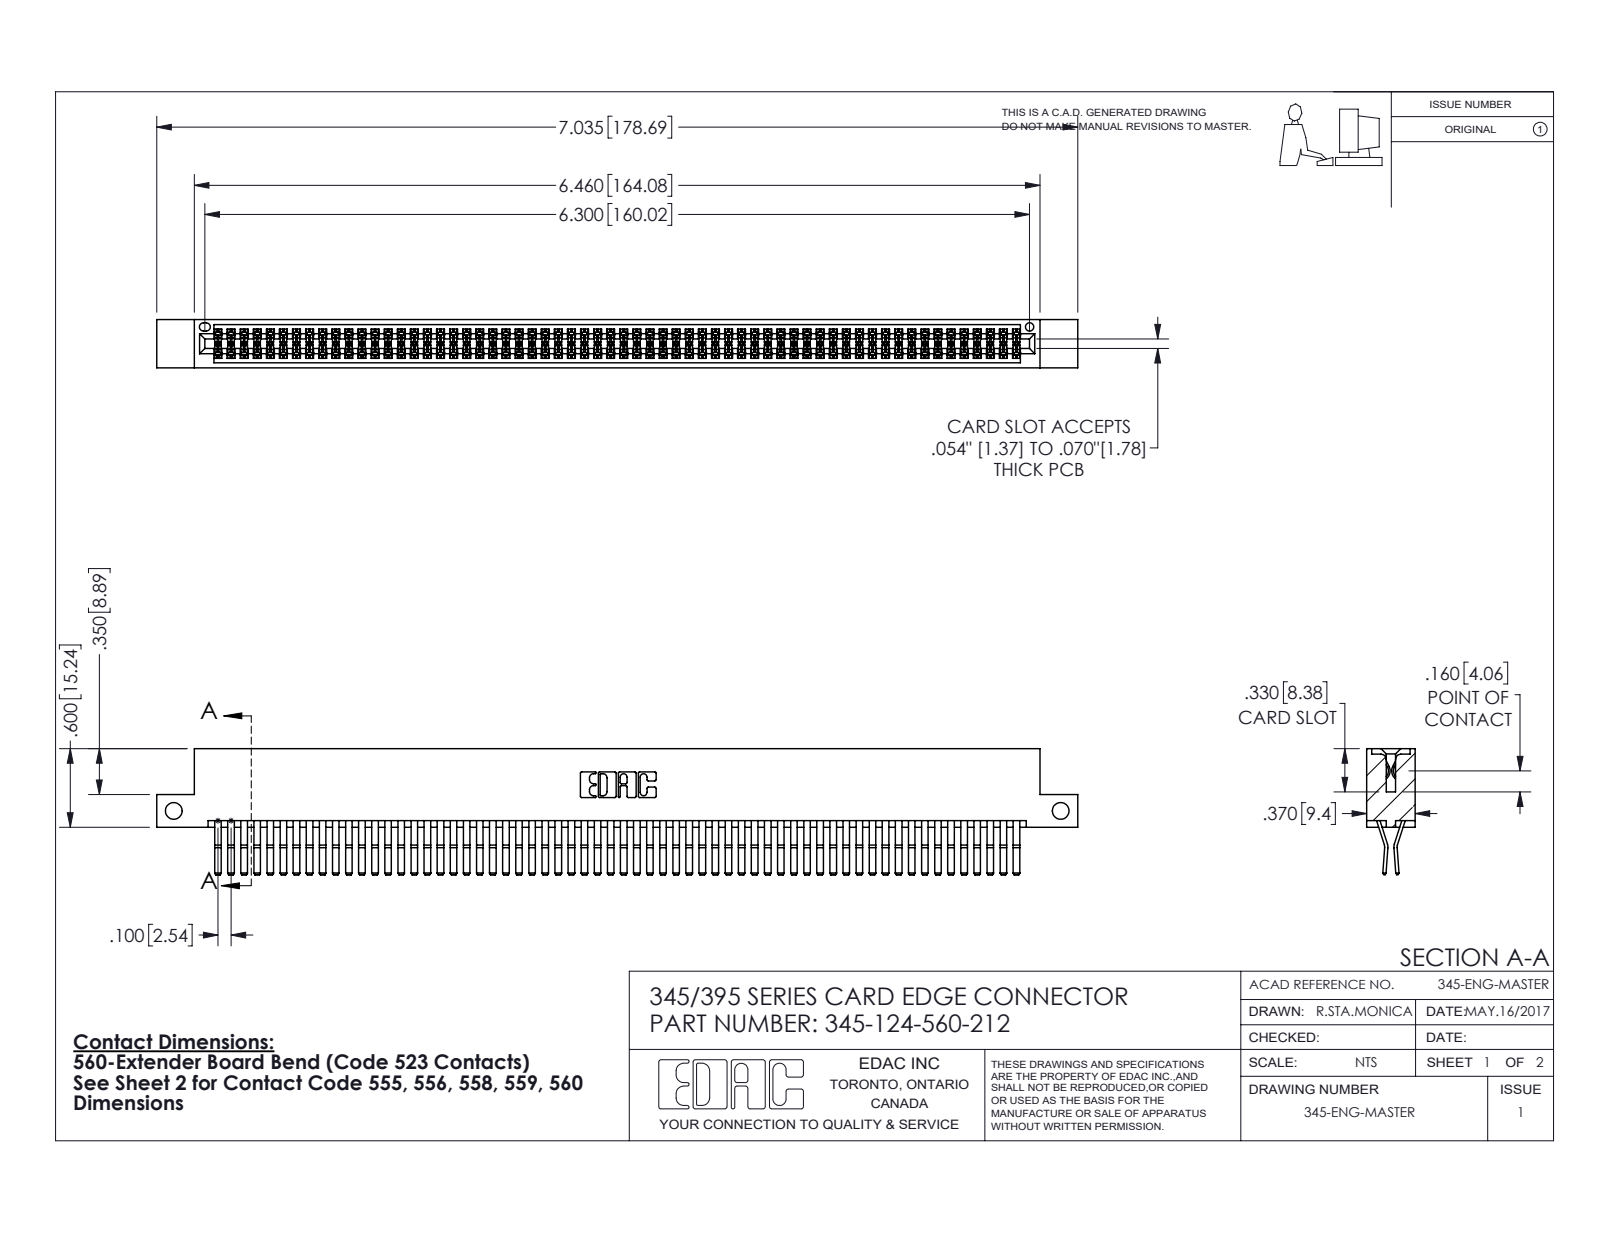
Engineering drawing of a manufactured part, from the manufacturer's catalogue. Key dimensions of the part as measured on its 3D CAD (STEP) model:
Part name (STEP PRODUCT): 345 Part_Flush Mounting Lugs - Side Mount; 345-124-560-212; 345-292-001_560 Tail
STEP written by: SolidWorks 2016 (CONFIG_CONTROL_DESIGN)
Units: inches
Bodies: 125 solids, 6574 faces (4172 planar, 2402 cylindrical, 0 other)
Overall size (bounding box): 7.035 × 0.962 × 0.37
Volume: 1.115 in³ · Surface area: 45.49 in²
Round holes (diameter × count): ⌀0.128 ×2, ⌀0.064 ×1
Partial cylindrical surfaces — rounded edges, fillets, slot ends (radius × count): R0.006 ×186, R0.01 ×22, R0.007 ×6, R0.031 ×6, R0.026 ×3, R0.01 ×2, R0.014 ×2, R0.019 ×2
Main face-to-face distances: 0.025, 0.298, 0.072, 0.37, 0.2, 0.098, 0.272, 0.225, 0.175, 0.149
Hole centre spacings: 6.775
